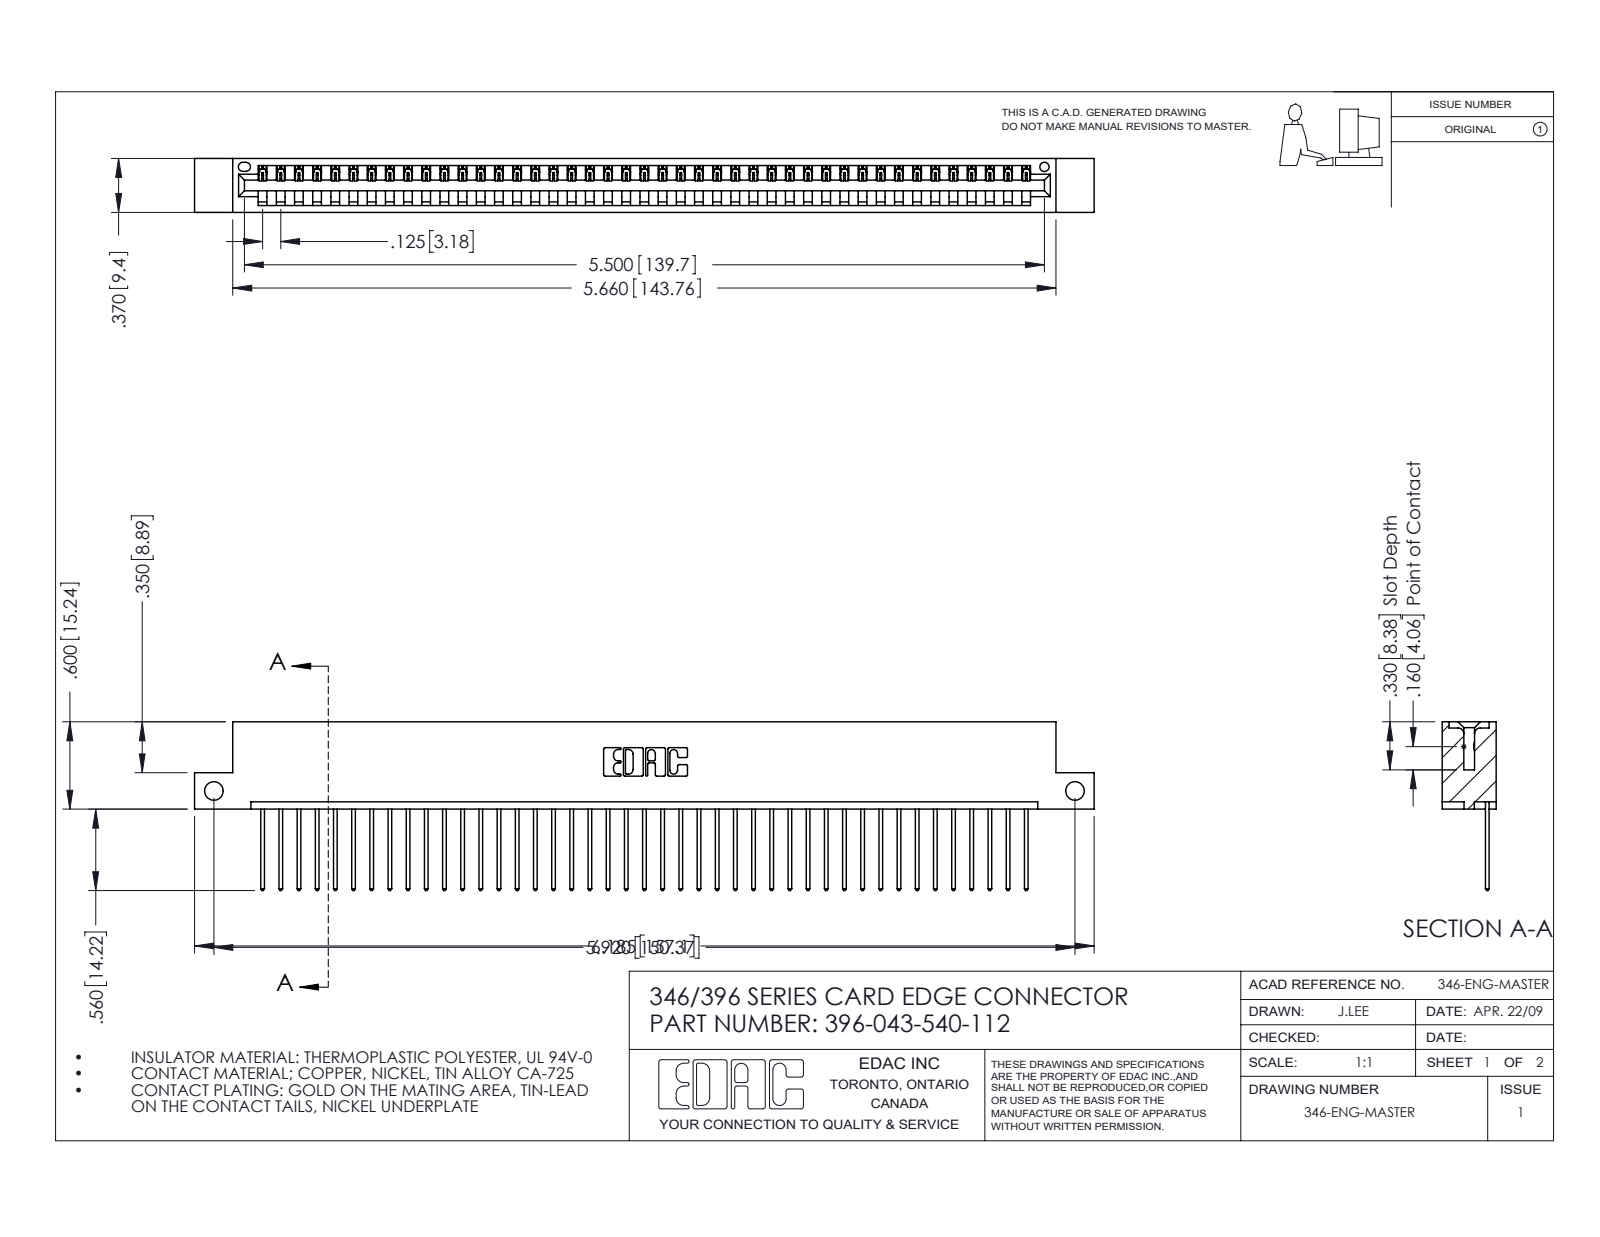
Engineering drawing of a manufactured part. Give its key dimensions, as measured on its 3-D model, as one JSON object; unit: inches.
{"part_name": "346 Part_Flush Mounting Lugs - Side Mount; 396-043-540-112; 345-292-001_345-293-140", "step_written_by": "SolidWorks 2016 (CONFIG_CONTROL_DESIGN)", "units": "inches", "bodies": {"solids": 44, "faces": 2616, "planar": 1796, "cylindrical": 820, "other": 0}, "overall_size": [6.185, 1.16, 0.37], "volume_in3": 0.916, "surface_area_in2": 29.54, "round_holes": [[0.128, 2], [0.064, 1]], "partial_cylinders_radius": [[0.006, 86], [0.01, 86], [0.01, 22], [0.007, 6], [0.031, 6], [0.026, 3], [0.031, 2], [0.04, 2]], "face_to_face_distances": [0.048, 0.322, 0.37, 0.25, 0.072, 0.298, 0.025, 0.148, 0.222, 0.1], "hole_center_spacings": [5.92]}
